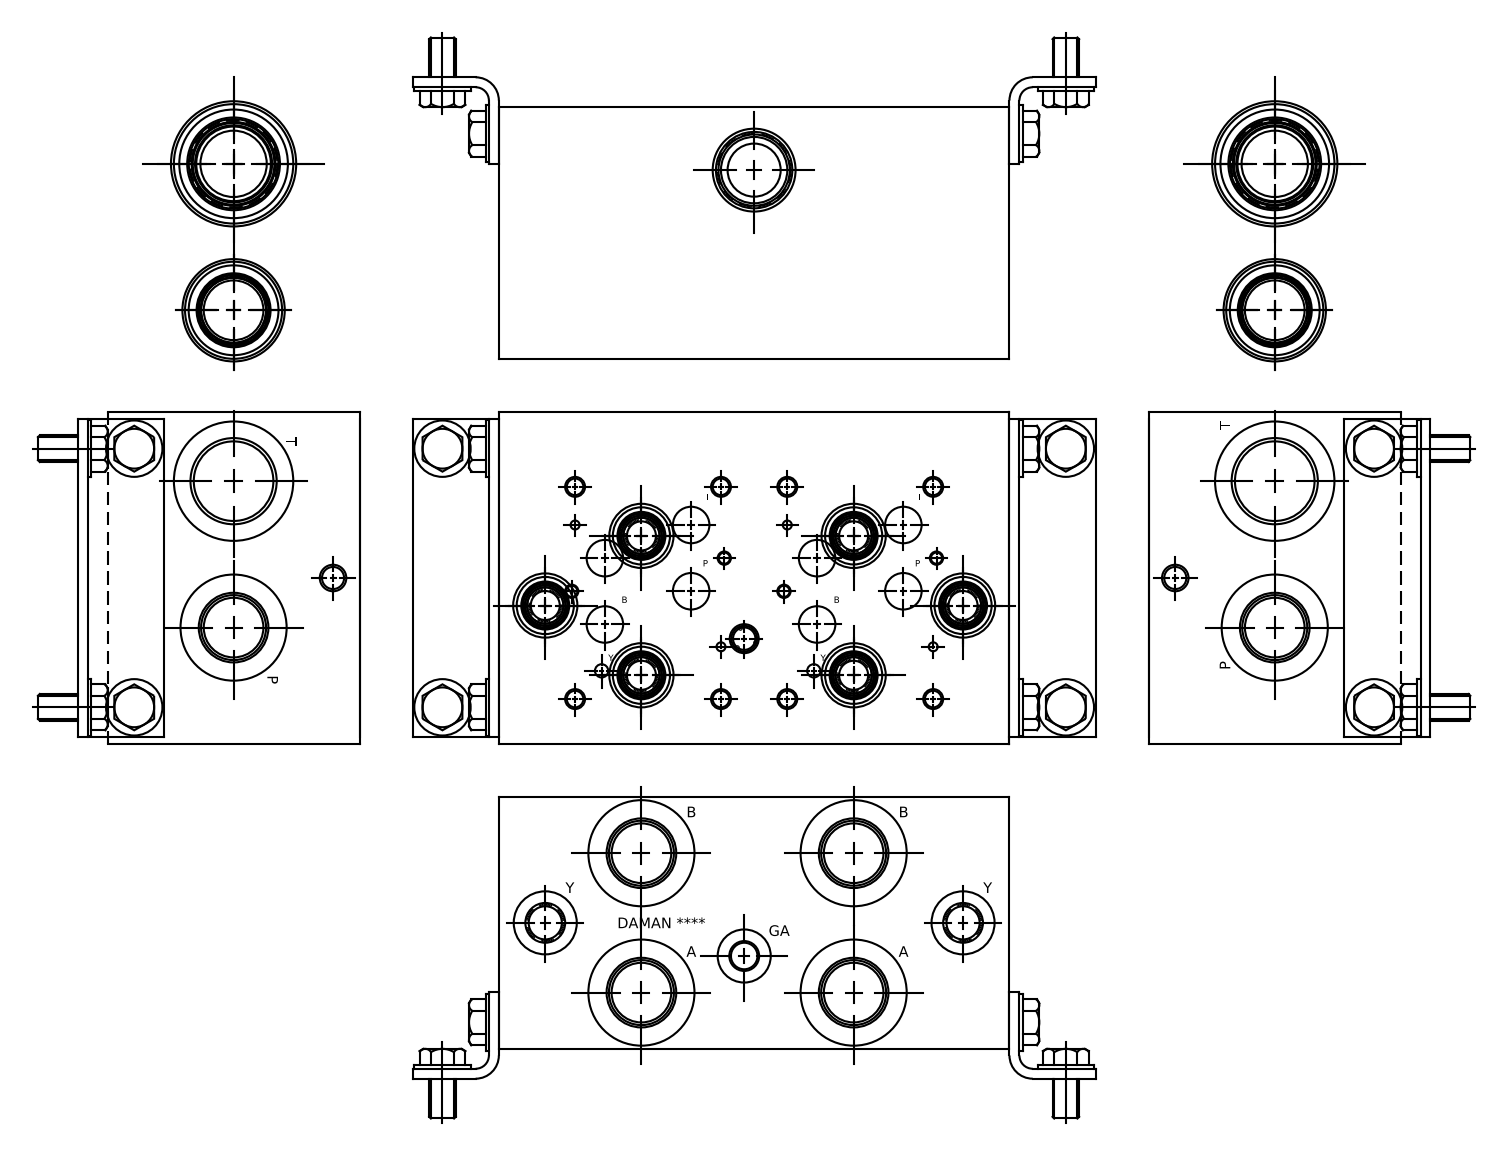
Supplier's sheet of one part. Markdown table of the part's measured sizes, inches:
| quantity | value |
| --- | --- |
| part name | d7hp24ss_3D |
| STEP written by | Autodesk Inventor 2009 (AUTOMOTIVE_DESIGN) |
| units | inches |
| bodies | 1 solid, 272 faces (61 planar, 111 cylindrical, 100 other) |
| overall size | 9.625 × 6.25 × 4.75 |
| volume | 253.2 in³ |
| surface area | 392.2 in² |
| round holes (diameter × count) | 0.75 × 10, 0.312 × 8, 0.375 × 8, 1.063 × 5, 1.231 × 5, 1.313 × 5, 1.398 × 5, 1.928 × 5, 0.172 × 4, 0.201 × 4, 0.25 × 4, 0.422 × 4 |
| main face-to-face distances | 4.75, 6.25, 9.625, 0.03, 6.22, 9.595, 9.565, 0.62, 0.161, 0.131 |
| hole center spacings | 4, 1.25, 4.854, 0.884, 2.25, 2.574, 2.75, 3.432 |
